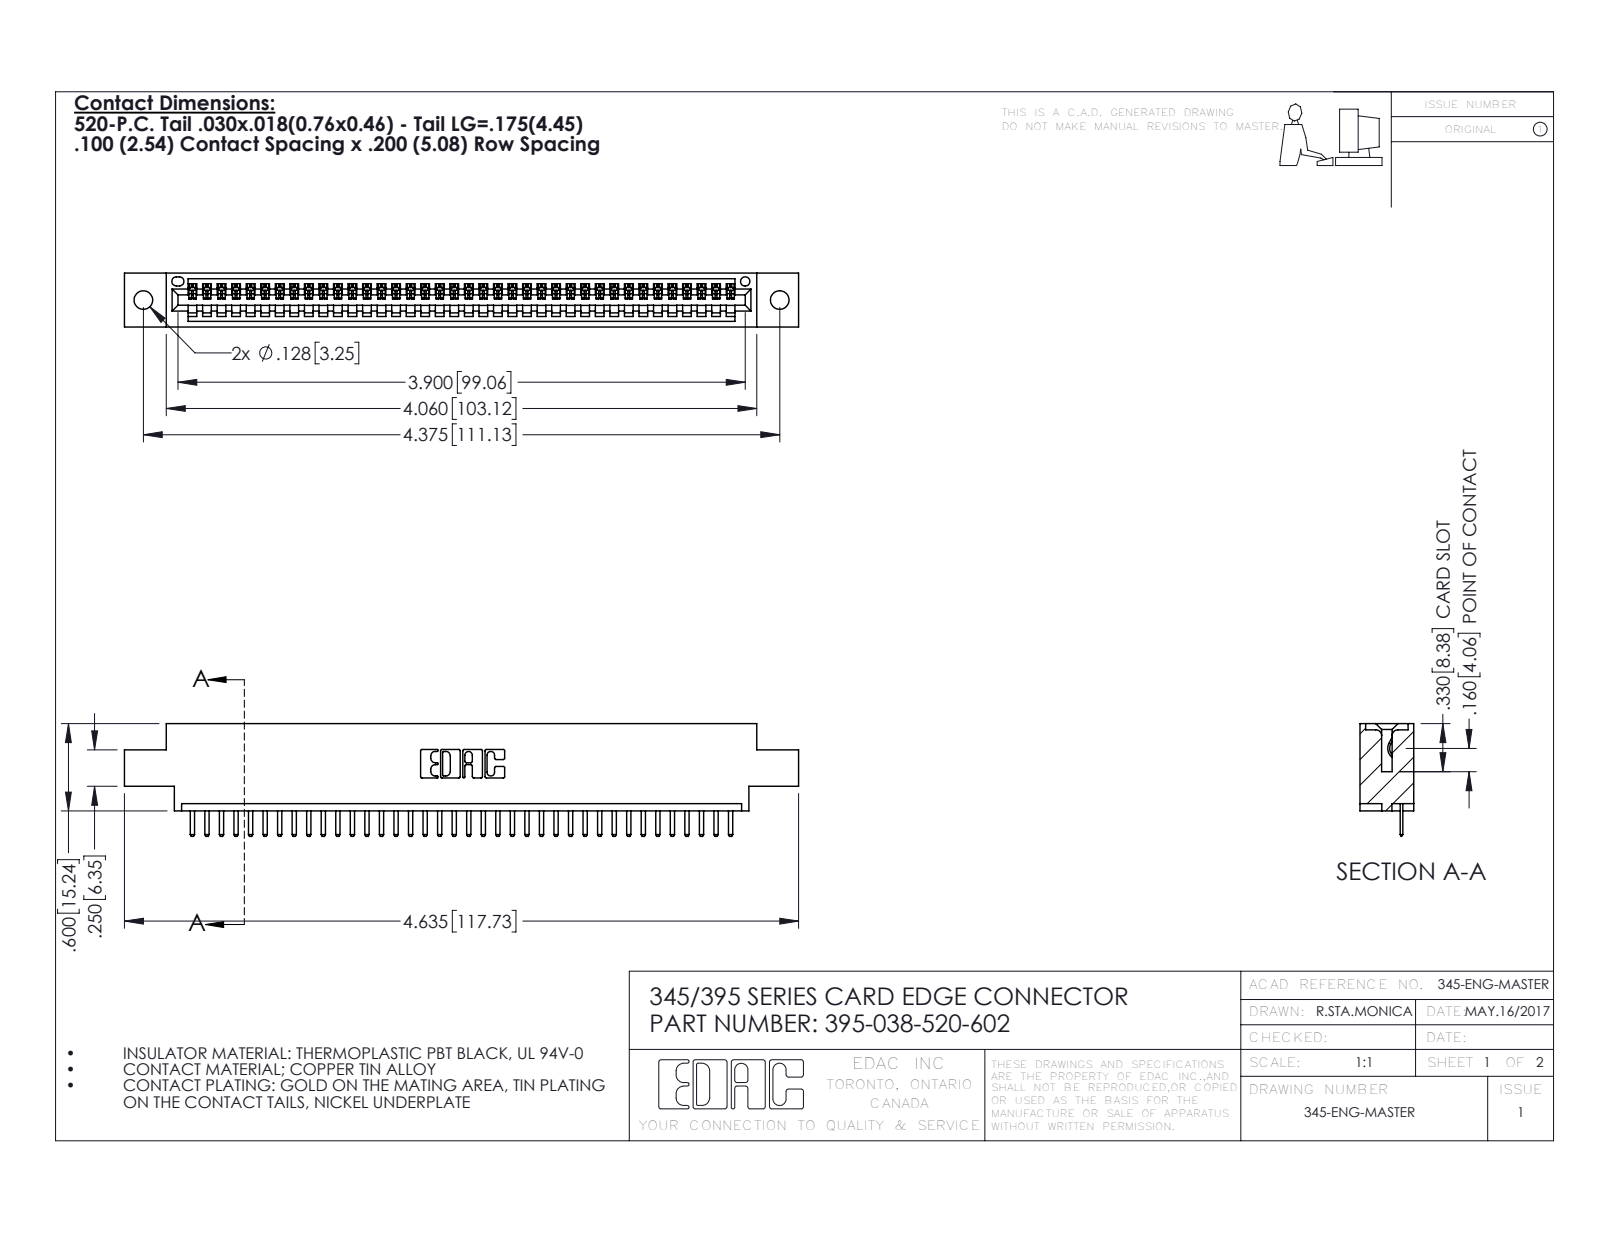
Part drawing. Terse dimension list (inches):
name: 345 Part_0.170 Offset - 0.128 Dia; 395-038-520-602; 345-292-001_345-293-120
written by: SolidWorks 2016 (CONFIG_CONTROL_DESIGN)
unit: in
bodies: 39 solids, 2486 faces (1680 planar, 806 cylindrical, 0 other)
size: 4.635 × 0.775 × 0.37
volume: 0.665 in³; area: 21.57 in²
holes: 2× ⌀0.128, 1× ⌀0.064
rounds: 78× R0.01, 76× R0.006, 22× R0.01, 6× R0.007, 6× R0.031, 3× R0.026, 2× R0.031, 2× R0.04
face distances: 0.298, 0.072, 0.37, 0.2, 0.098, 0.272, 0.025, 0.225, 0.072, 0.175
hole spacings: 0.27, 4.139, 4.375
